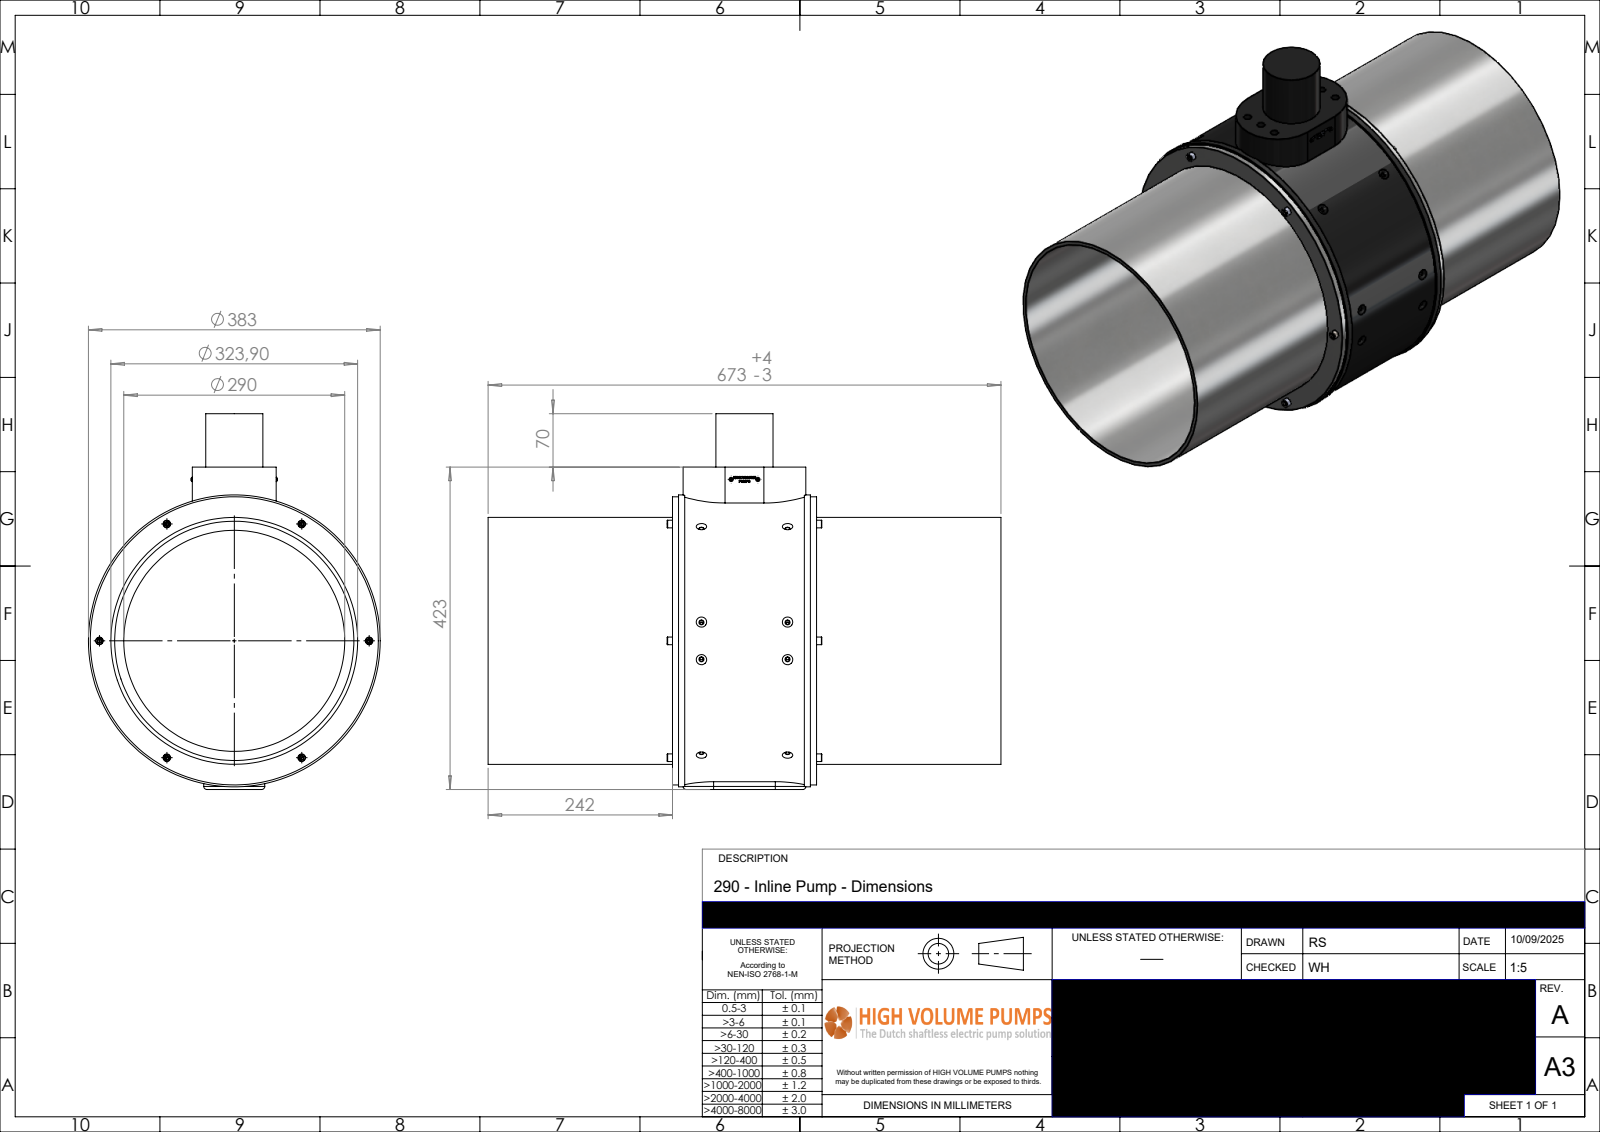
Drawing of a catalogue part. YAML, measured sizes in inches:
part_name: "P-290-030-rev-A-IP"
step_written_by: "SolidWorks 2024 (AUTOMOTIVE_DESIGN)"
units: inches
bodies: {solids: 1, faces: 809, planar: 551, cylindrical: 64, other: 194}
overall_size: [26.496, 19.409, 15.079]
volume: 725
surface_area: 2364
round_holes:
  - {diameter: 0.197, count: 16}
  - {diameter: 0.402, count: 6}
  - {diameter: 0.138, count: 2}
  - {diameter: 11.417, count: 1}
  - {diameter: 12.358, count: 1}
round_bosses_or_shafts:
  - {diameter: 0.394, count: 6}
  - {diameter: 0.456, count: 2}
  - {diameter: 0.224, count: 2}
  - {diameter: 15.079, count: 1}
  - {diameter: 14.882, count: 1}
  - {diameter: 12.752, count: 1}
  - {diameter: 2.953, count: 1}
partial_cylinders:
  - {radius: 0.157, count: 2}
  - {radius: 1.575, count: 2}
  - {radius: 2.165, count: 2}
face_to_face_distances: [7.441, 16.654, 0.315, 6.89, 0.551, 0.549, 6.341, 6.892, 9.528, 16.969]
hole_center_spacings: [4.449, 0.014, 0.984, 4.556, 1.969, 4.865, 1.378]
